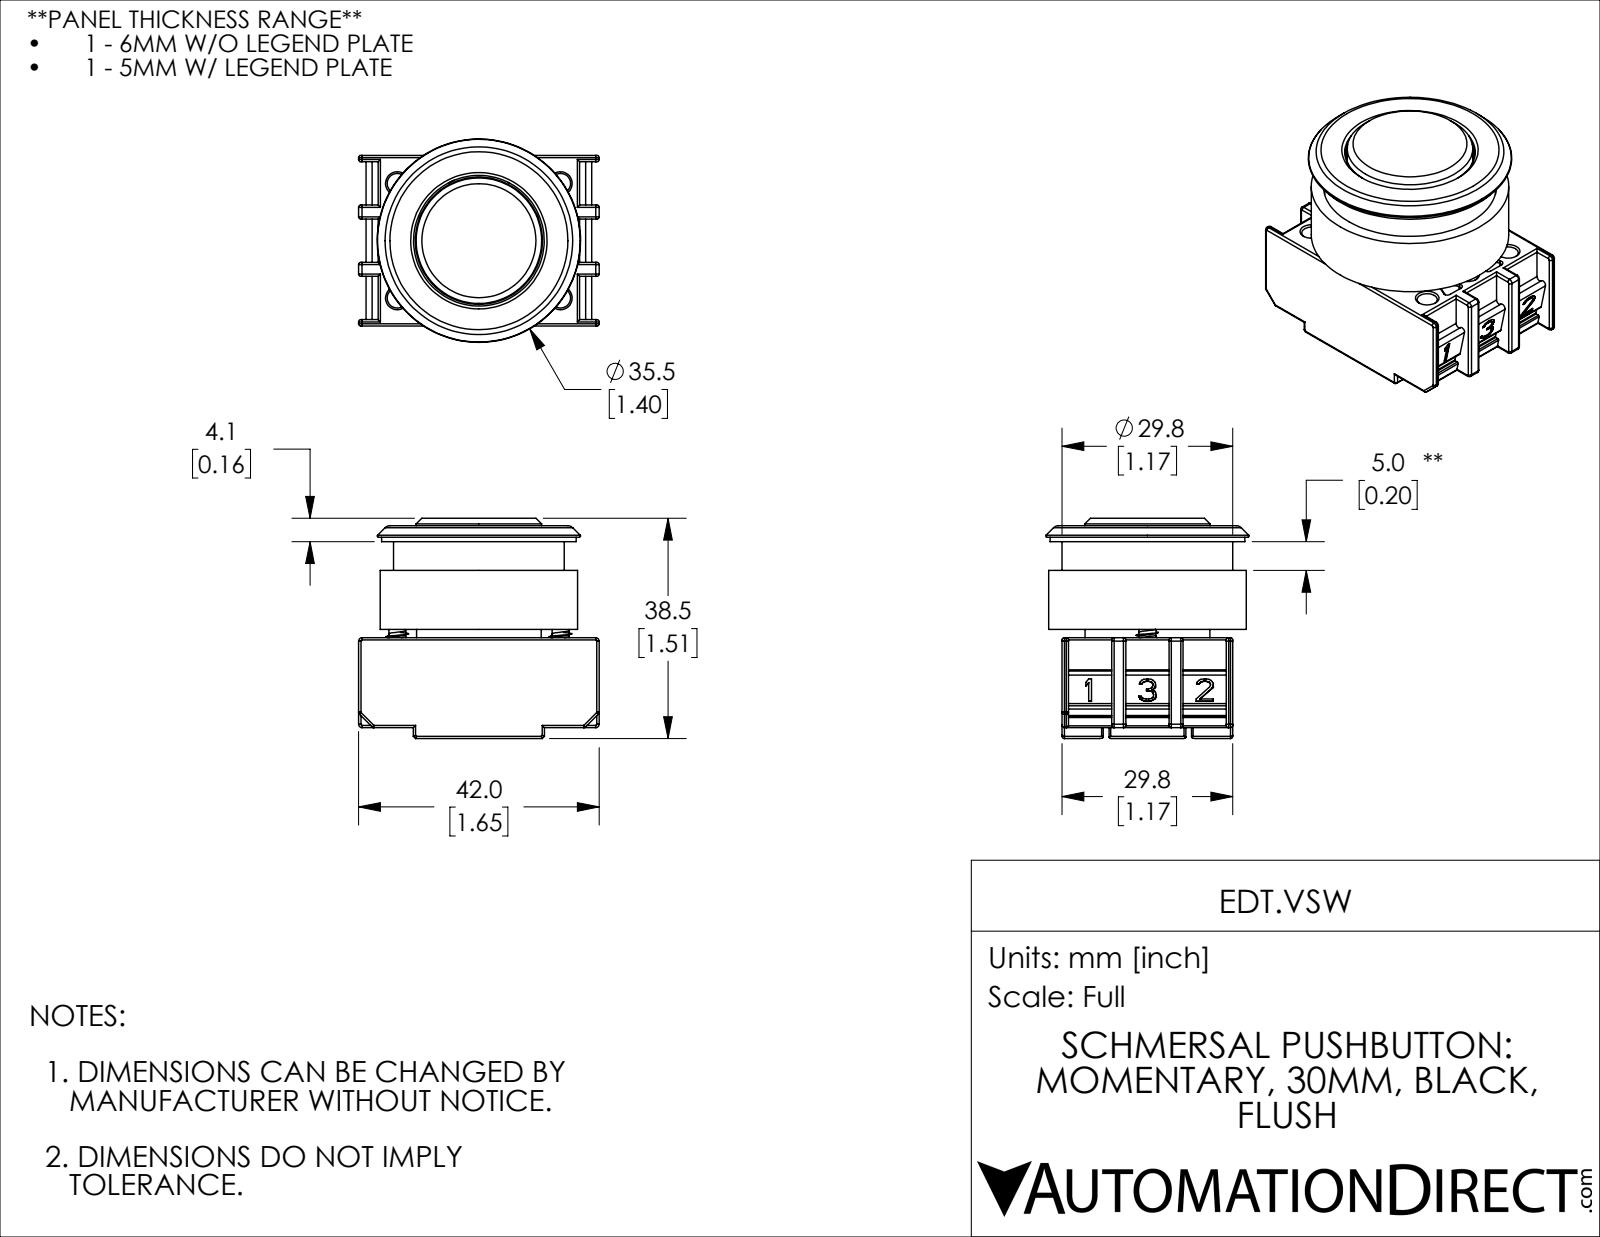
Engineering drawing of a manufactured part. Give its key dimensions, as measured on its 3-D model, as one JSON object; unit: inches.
{"part_name": "EDT.VSW", "step_written_by": "SolidWorks 2019 (CONFIG_CONTROL_DESIGN)", "units": "inches", "bodies": {"solids": 3, "faces": 1361, "planar": 509, "cylindrical": 460, "other": 392}, "overall_size": [1.654, 1.514, 1.398], "volume_in3": 1.379, "surface_area_in2": 31.76, "round_holes": [[0.138, 6], [0.203, 6], [0.161, 1], [0.492, 1], [0.709, 1], [0.756, 1], [0.874, 1], [0.898, 1], [0.953, 1], [1.024, 1], [1.063, 1], [1.189, 1]], "round_bosses_or_shafts": [[0.189, 2], [0.115, 2], [1.358, 1], [1.339, 1], [1.173, 1], [0.969, 1], [0.862, 1], [0.858, 1]], "partial_cylinders_radius": [[0.016, 112], [0.012, 48], [0.008, 24], [0.024, 8], [0.02, 6], [0.004, 2], [0.024, 2], [0.031, 2]], "face_to_face_distances": [1.173, 0.075, 0.764, 0.232, 0.161, 0.057, 0.638, 0.75, 0.394, 0.051], "hole_center_spacings": [0.394, 0.685, 1.189, 1.122, 0.561, 0.787, 1.371]}
